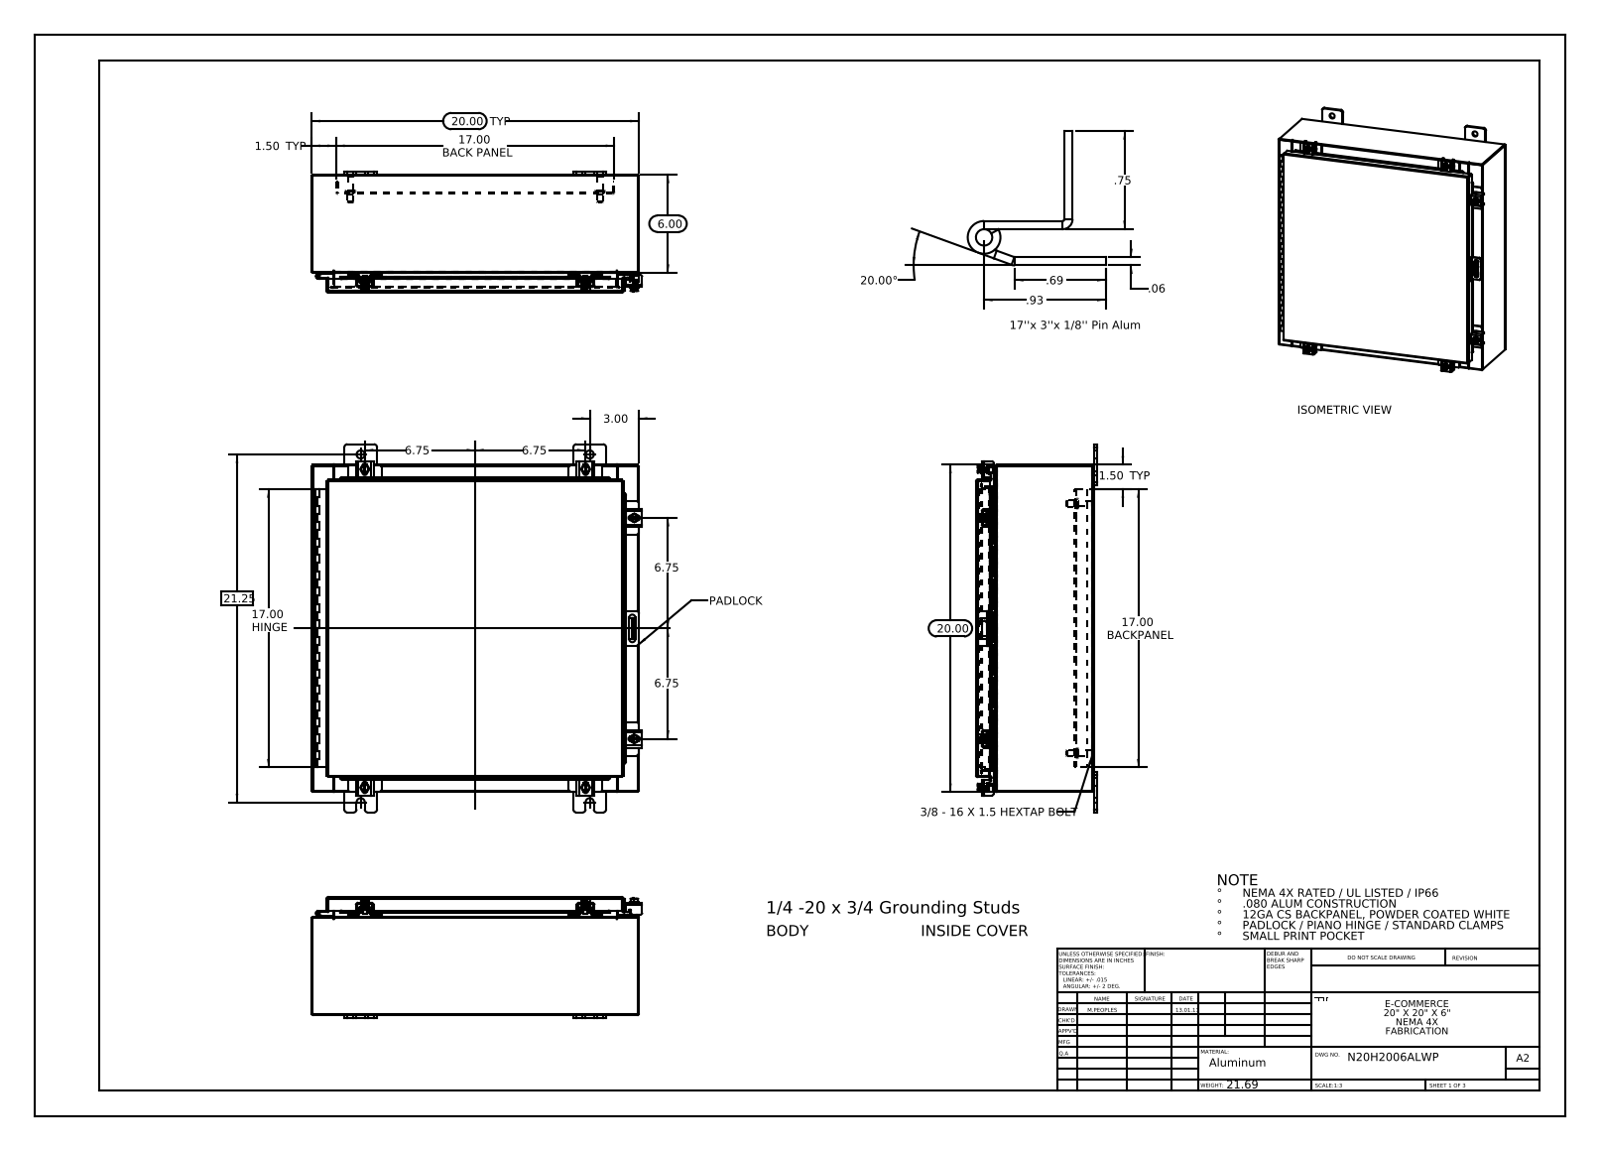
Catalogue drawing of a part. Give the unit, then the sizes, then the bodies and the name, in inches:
Units: inches
Overall size (bounding box): 22.5 × 20.211 × 7.389
Round holes (diameter × count): ⌀0.5 ×8, ⌀0.213 ×6, ⌀0.26 ×6, ⌀0.125 ×2, ⌀0.125 ×1
Round bosses / shafts (diameter × count): ⌀0.25 ×7, ⌀0.5 ×6, ⌀0.399 ×6, ⌀0.625 ×4, ⌀0.375 ×4, ⌀0.33 ×4
Partial cylindrical surfaces — rounded edges, fillets, slot ends (radius × count): R0.06 ×30, R0.013 ×25, R0.19 ×24, R0.088 ×21, R0.12 ×12, R0.141 ×12, R0.125 ×10, R0.05 ×9
Main face-to-face distances: 0.075, 7.126, 19.925, 7.201, 7.051, 0.104, 1, 1.075, 6.051, 6.126
Hole centre spacings: 17.373, 14.528, 16.742, 22.532, 13.5, 0.431, 0.934, 1.858
Volume: 148.9 in³ · Surface area: 3 740 in²
Bodies: 47 solids, 1613 faces (860 planar, 657 cylindrical, 96 other)
Part name (STEP PRODUCT): N20H2006ALWP Mounting Studs; N20H2006ALWP Clamp Top; N20H2006ALWP Body; N20H2006ALWP Top (+8 more)
STEP written by: SolidWorks 2013 (CONFIG_CONTROL_DESIGN)
